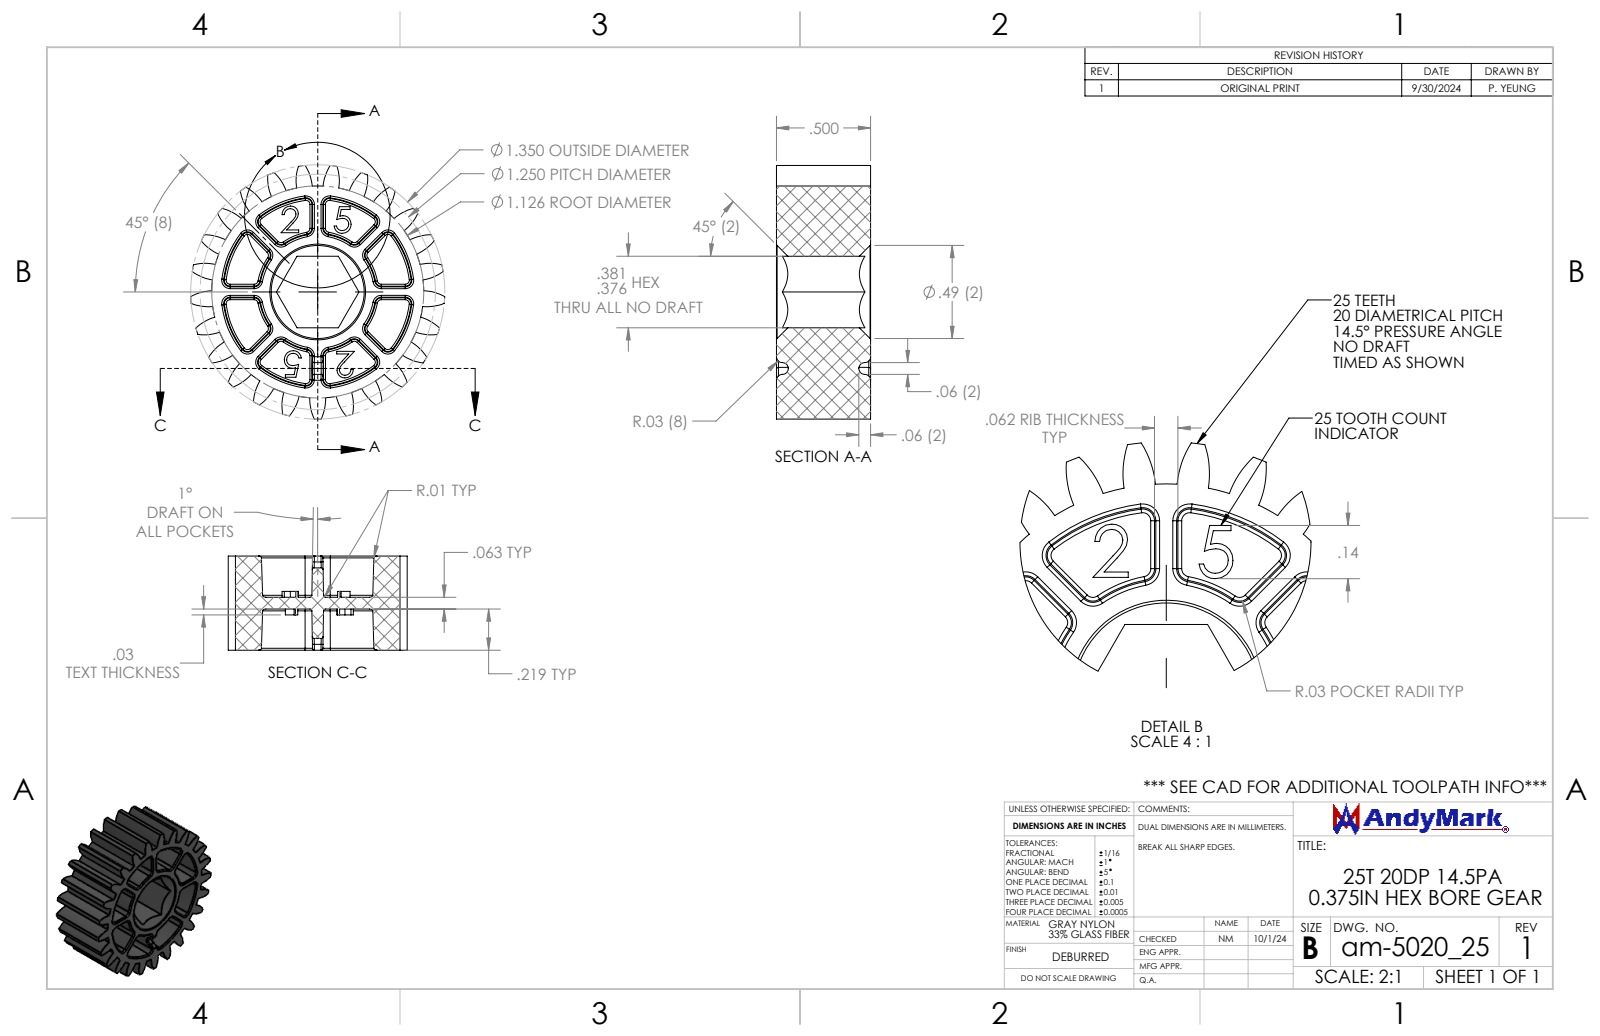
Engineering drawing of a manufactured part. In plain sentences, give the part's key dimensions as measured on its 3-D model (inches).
The part is named "am-5020_25 25T 20DP 14.5PA 0.50 IN FW 0.375 Hex Gear". Its 3-D file was written by "SolidWorks 2024 (AUTOMOTIVE_DESIGN)". It is 1 solid with 696 faces: 112 planar, 176 cylindrical and 408 other. Overall it measures 1.349 by 1.347 by 0.5 inches. Its volume is 0.358 cubic inches and its surface area 9.775 square inches. Partial cylindrical surfaces (rounded edges, fillets, slot ends): 50 of radius 0.25, 34 of radius 0.01, 6 of radius 0.031, 1 of radius 0.563, 1 of radius 0.675. The main face-to-face distances are 0.219, 0.281, 0.5, 0.064, 0.062, 0.38, 0.187, 0.313, 0.031, 0.094.
